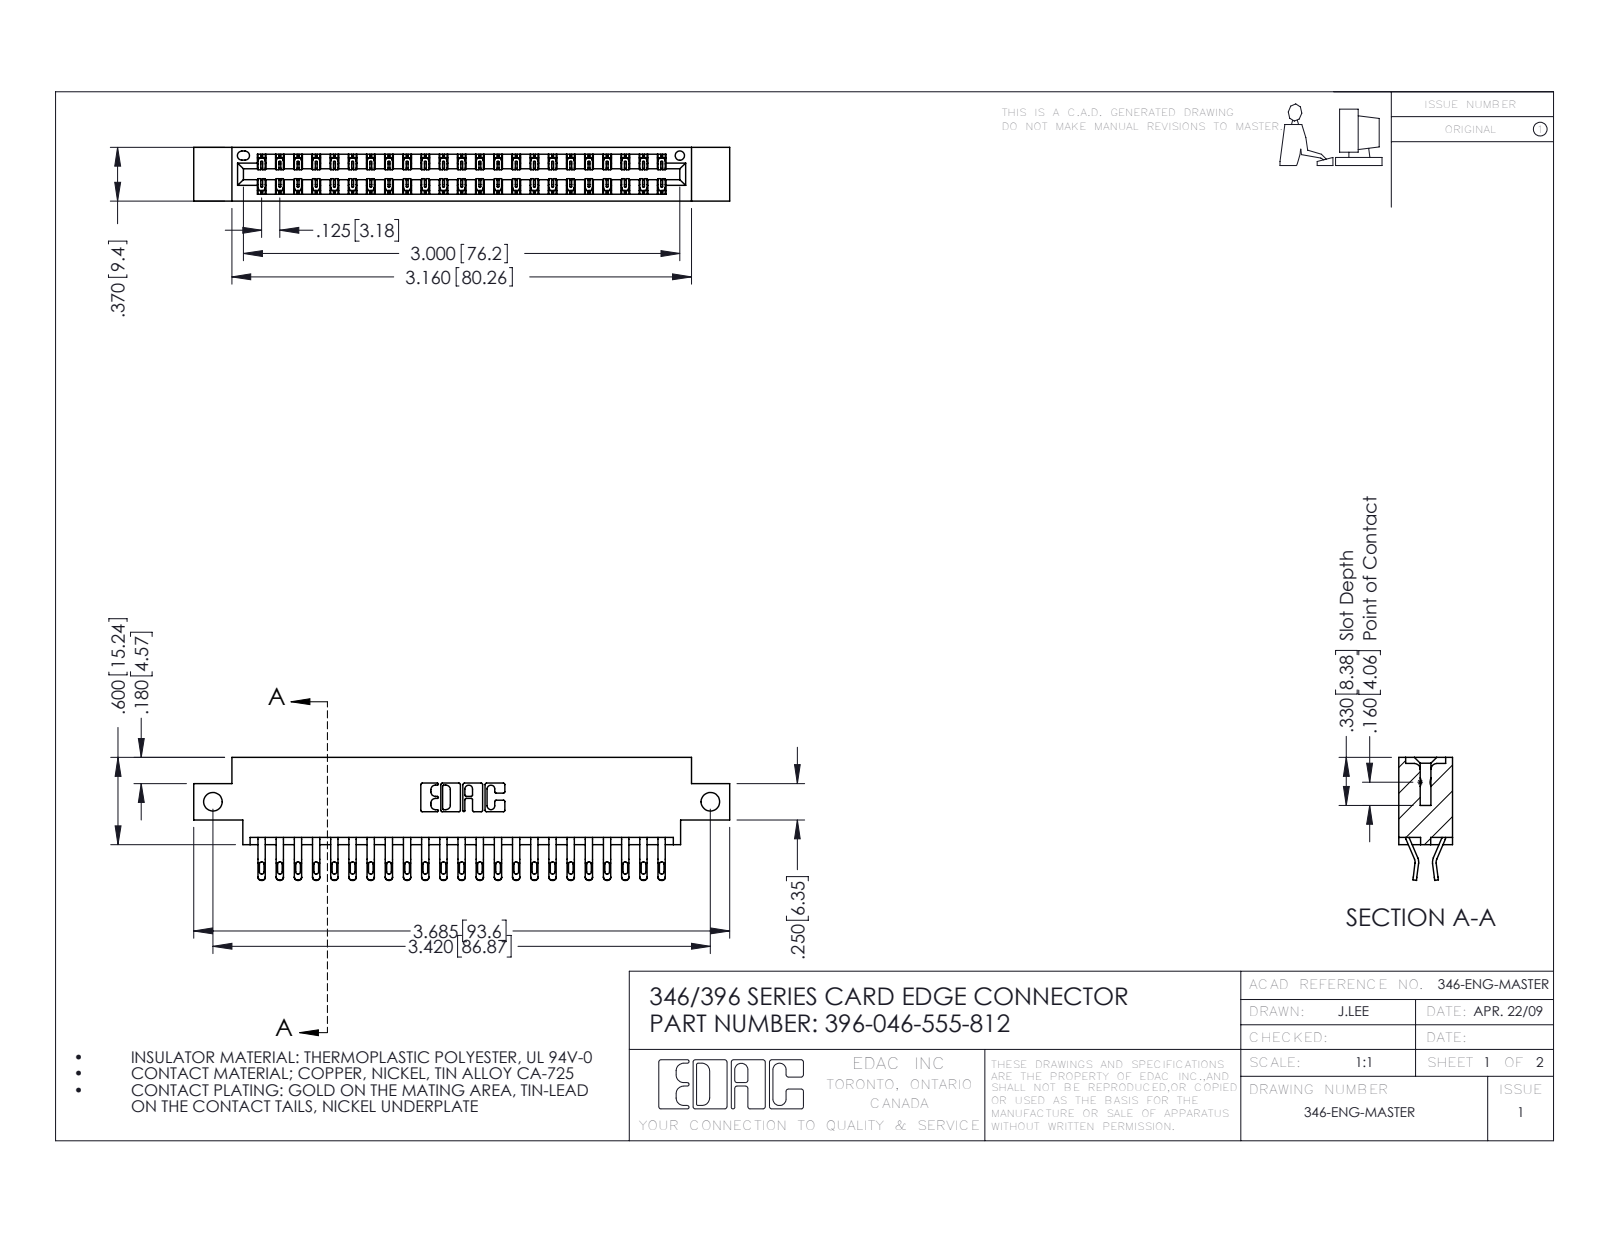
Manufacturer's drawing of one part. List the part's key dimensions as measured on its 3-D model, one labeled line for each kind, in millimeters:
Part name (STEP PRODUCT): 396-046-555-812; 346 Part_0.170 Offset - Side Mount; 345-292-001_555 Tail
STEP written by: SolidWorks 2016 (CONFIG_CONTROL_DESIGN)
Units: millimetres
Bodies: 47 solids, 2794 faces (1598 planar, 1196 cylindrical, 0 other)
Overall size (bounding box): 93.6 × 21.5 × 9.4
Volume: 8 870 mm³ · Surface area: 12 410 mm²
Round holes (diameter × count): ⌀3.3 ×2, ⌀1.6 ×1
Partial cylindrical surfaces — rounded edges, fillets, slot ends (radius × count): R0.4 ×92, R0.5 ×92, R0.2 ×69, R0.3 ×22, R0.2 ×6, R0.8 ×6, R0.7 ×3, R0.3 ×2
Main face-to-face distances: 1.2, 8.2, 9.4, 6.4, 0.6, 1.8, 7.6, 7, 3.8, 5.6
Hole centre spacings: 86.9
